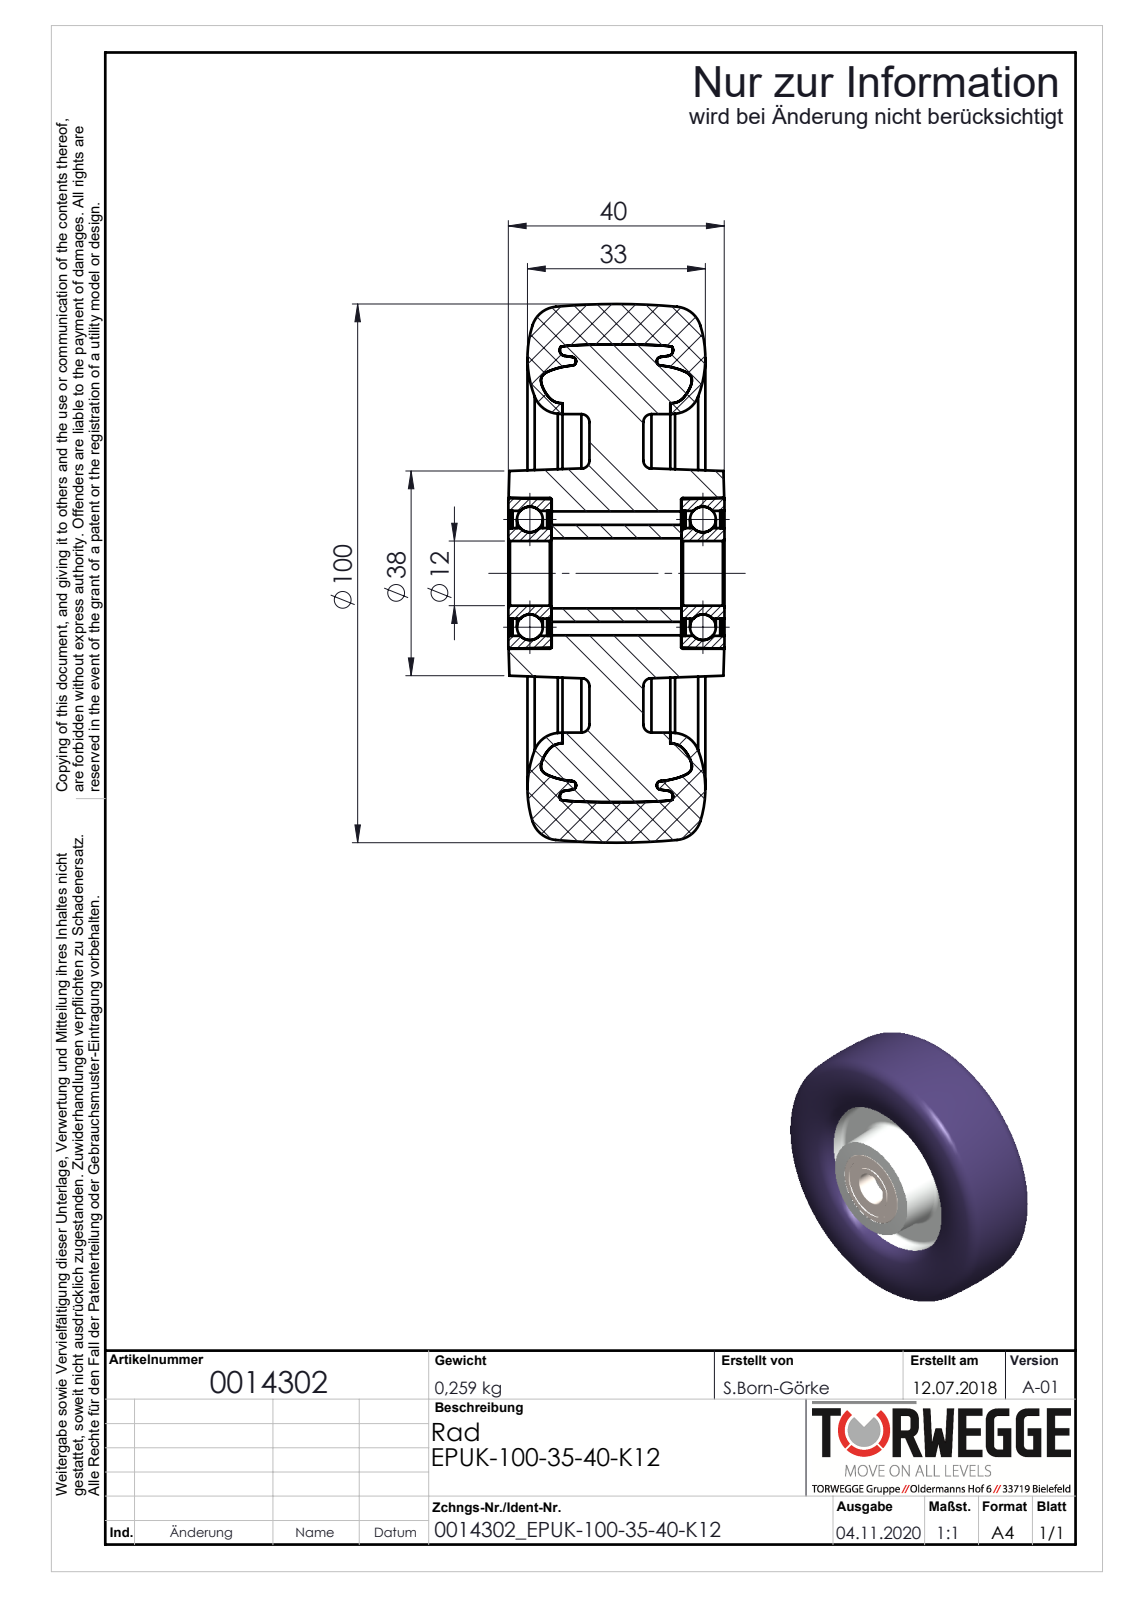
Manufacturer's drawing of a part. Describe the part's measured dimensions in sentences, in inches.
The part is named "0014302". Its 3-D file was written by "SolidWorks 2018 (AUTOMOTIVE_DESIGN)". It is 12 solids with 258 faces: 54 planar, 58 cylindrical and 146 other. Overall it measures 3.937 by 3.937 by 1.579 inches. Its volume is 12.69 cubic inches and its surface area 70.19 square inches. Round holes: 1 of diameter 0.472, 1 of diameter 0.512, 1 of diameter 0.661, 1 of diameter 0.906, 1 of diameter 0.913, 1 of diameter 2.328. Round bosses or shafts: 1 of diameter 1.102, 1 of diameter 0.709. Partial cylindrical surfaces (rounded edges, fillets, slot ends): 1 of radius 1.555. The main face-to-face distances are 1.264, 0.394, 0.031, 0.02, 0.283, 0.303, 0.272, 0.278, 0.671, 0.315.
